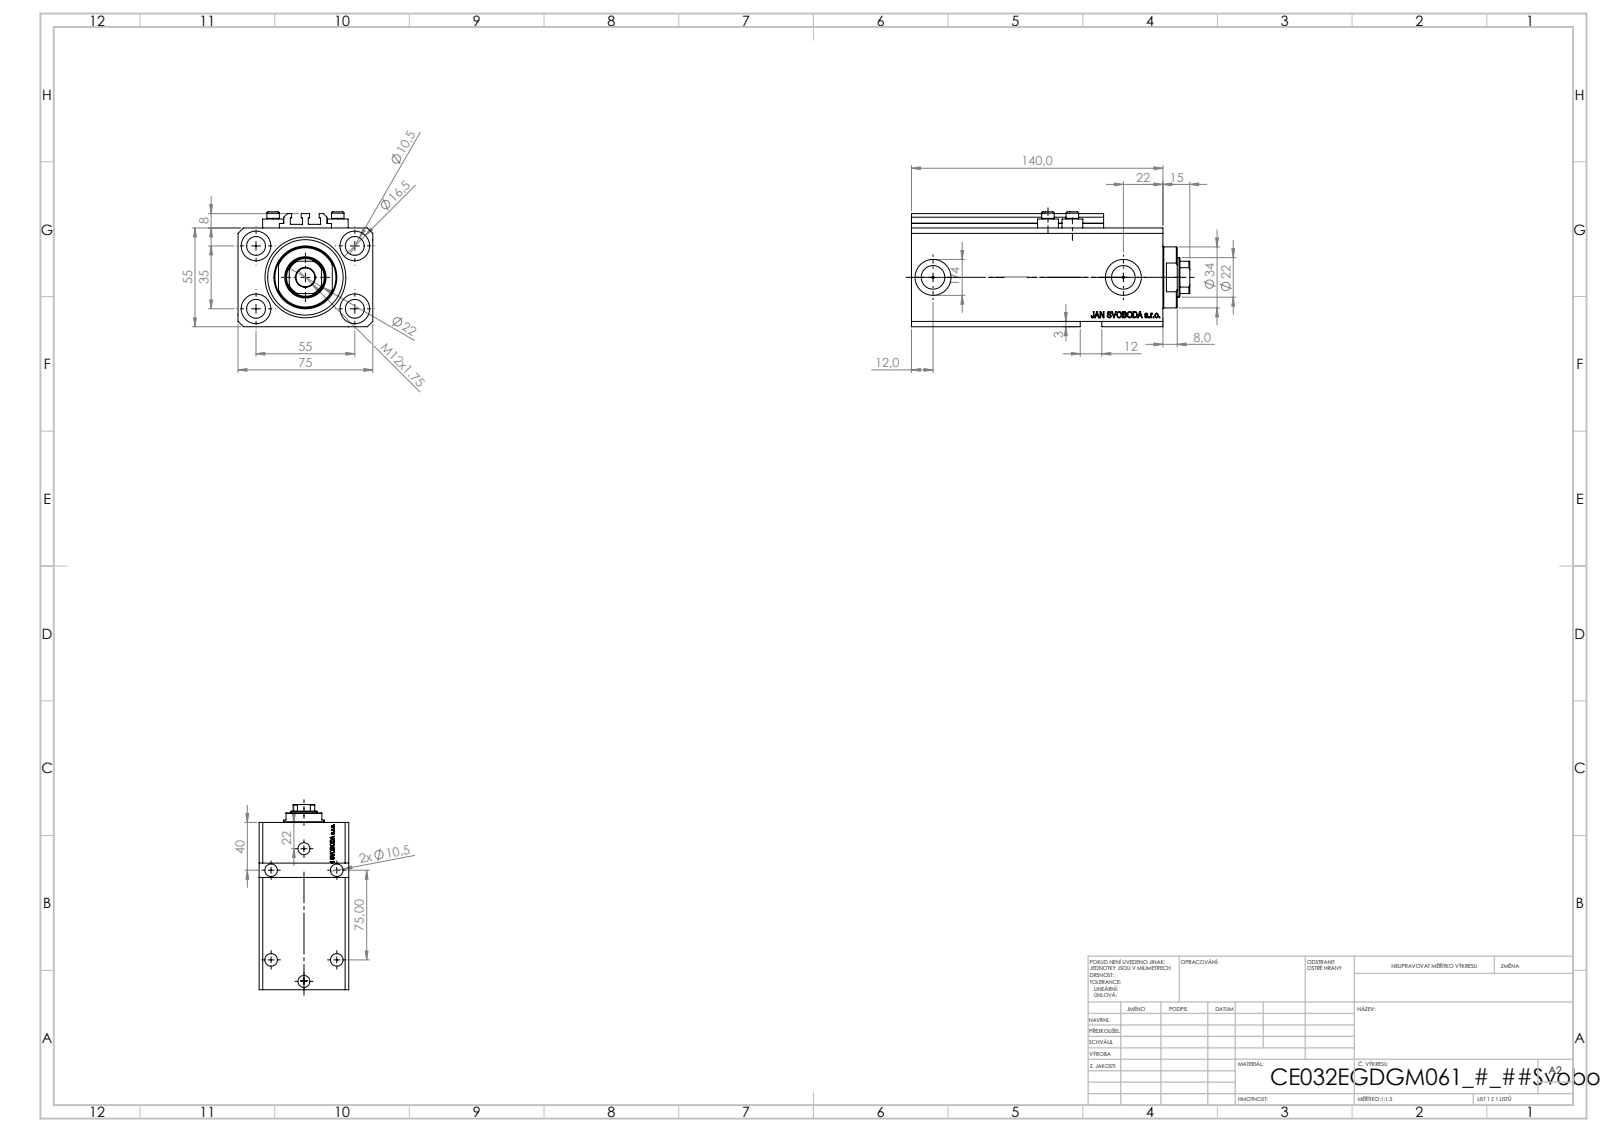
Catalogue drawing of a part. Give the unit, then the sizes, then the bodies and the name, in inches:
Units: inches
Overall size (bounding box): 6.102 × 2.953 × 2.52
Round holes (diameter × count): ⌀0.413 ×9, ⌀0.049 ×4, ⌀0.157 ×4, ⌀0.65 ×4, ⌀0.394 ×2, ⌀0.518 ×2, ⌀0.787 ×2, ⌀0.866 ×1, ⌀1.26 ×1, ⌀1.772 ×1
Round bosses / shafts (diameter × count): ⌀0.457 ×4, ⌀0.276 ×4, ⌀1.339 ×1
Partial cylindrical surfaces — rounded edges, fillets, slot ends (radius × count): R0.008 ×10, R0.413 ×1
Main face-to-face distances: 2.165, 2.953, 0.591, 0.39, 5.512, 4.921, 0.118, 2.244, 4.531, 5.122
Hole centre spacings: 1.283, 1.294, 2.165, 3.818, 0.535, 0.555, 1.016, 1.283
Volume: 29.39 in³ · Surface area: 180.5 in²
Bodies: 8 solids, 1100 faces (518 planar, 158 cylindrical, 424 other)
Part name (STEP PRODUCT): ALLEN BOLT V250CE; V250CE_C_VCP; V250CE_E_Body; V250CE_VC_E
STEP written by: SolidWorks 2019 (CONFIG_CONTROL_DESIGN)
